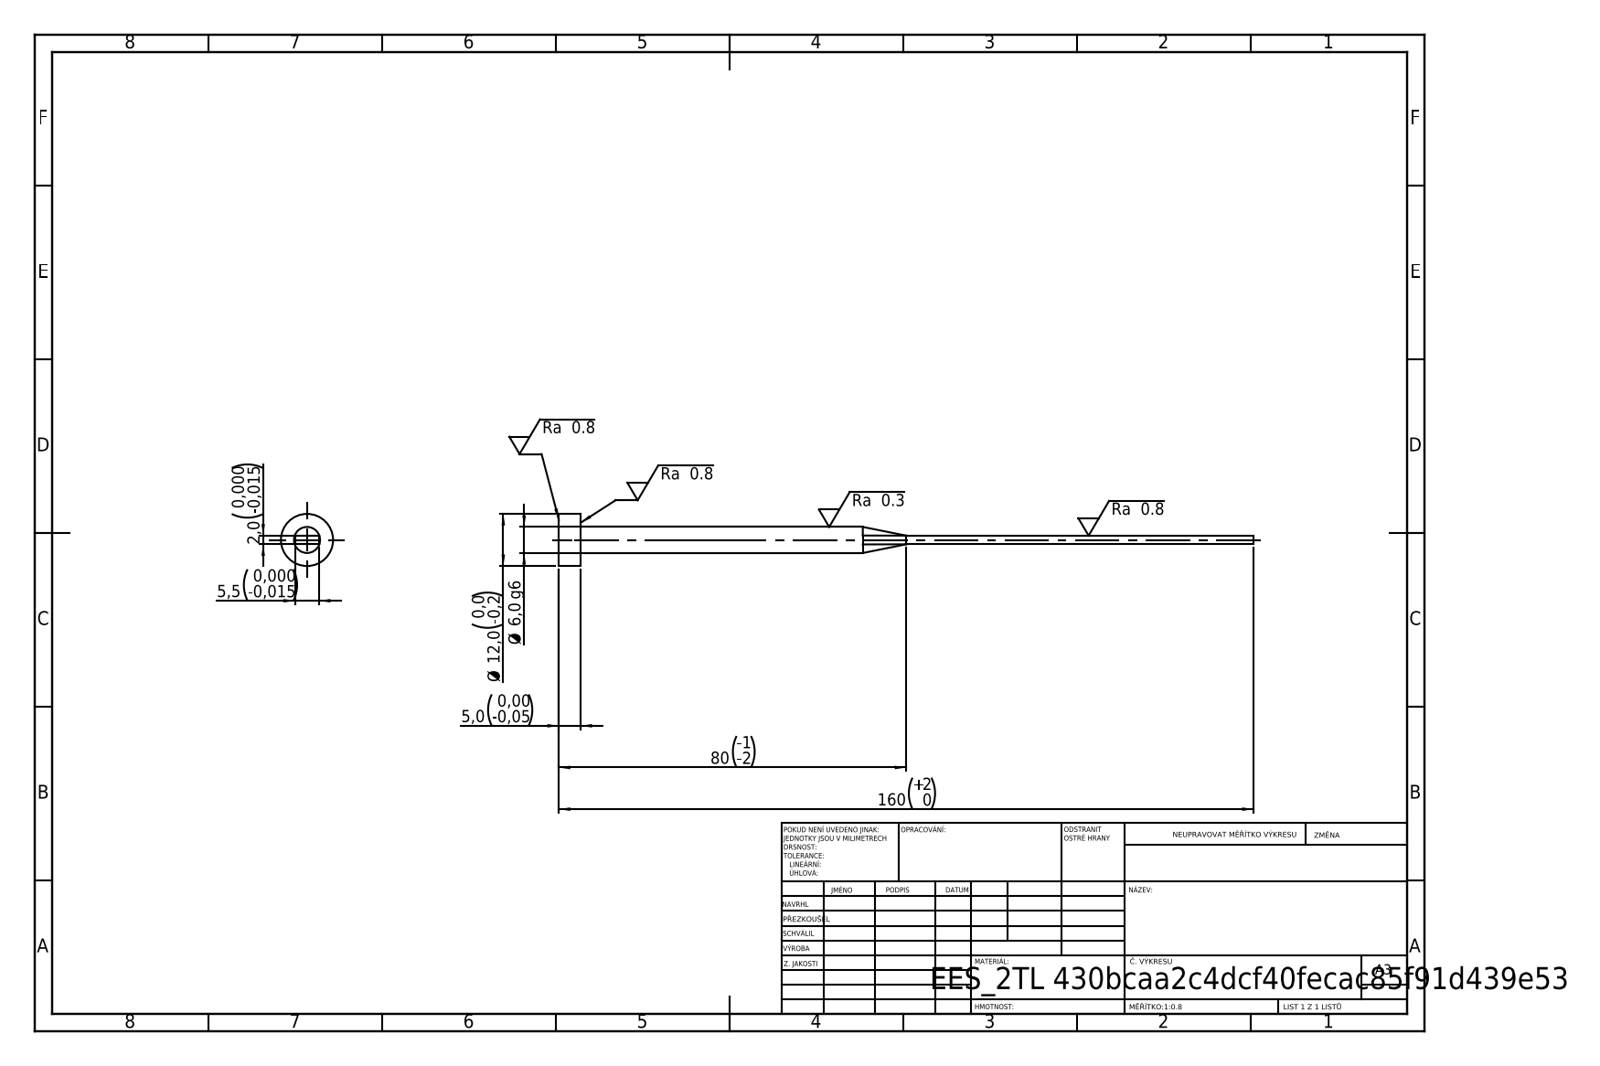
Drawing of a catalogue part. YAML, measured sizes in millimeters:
step_written_by: "SolidWorks 2019 (CONFIG_CONTROL_DESIGN)"
units: millimeters
bodies: {solids: 1, faces: 15, planar: 7, cylindrical: 4, other: 4}
overall_size: [160, 12, 12]
volume: 3475
surface_area: 2988
round_bosses_or_shafts:
  - {diameter: 12, count: 1}
  - {diameter: 6, count: 1}
face_to_face_distances: [2, 5.5, 5, 160, 155]
